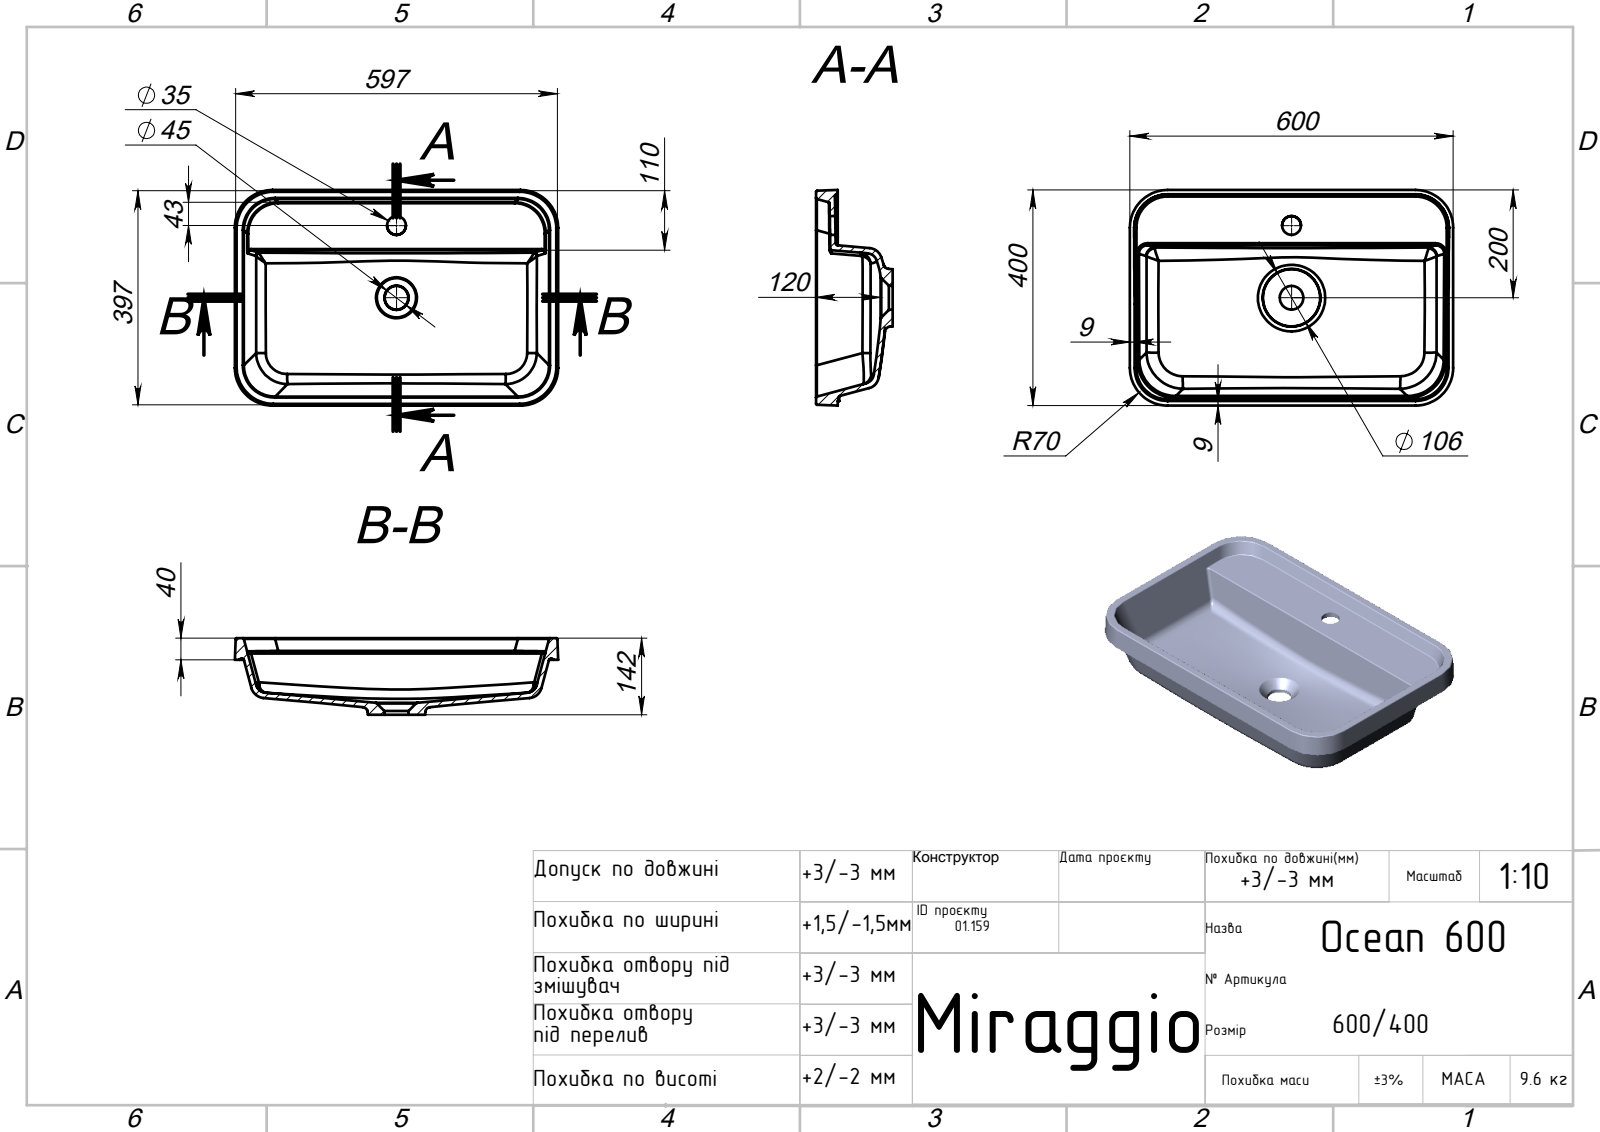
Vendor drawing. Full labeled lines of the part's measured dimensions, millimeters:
Part name (STEP PRODUCT): Ocean 600
STEP written by: SolidWorks 2020 (AUTOMOTIVE_DESIGN)
Units: millimetres
Bodies: 1 solid, 121 faces (22 planar, 42 cylindrical, 57 other)
Overall size (bounding box): 600 × 400 × 142
Volume: 4 160 000 mm³ · Surface area: 759 721 mm²
Round holes (diameter × count): ⌀35 ×1
Partial cylindrical surfaces — rounded edges, fillets, slot ends (radius × count): R5 ×16, R70 ×6, R2 ×4, R60 ×4, R62 ×4, R1 ×3, R6 ×2, R16 ×2
Main face-to-face distances: 10, 9.99, 5, 15, 102, 107, 117, 142, 40, 35
